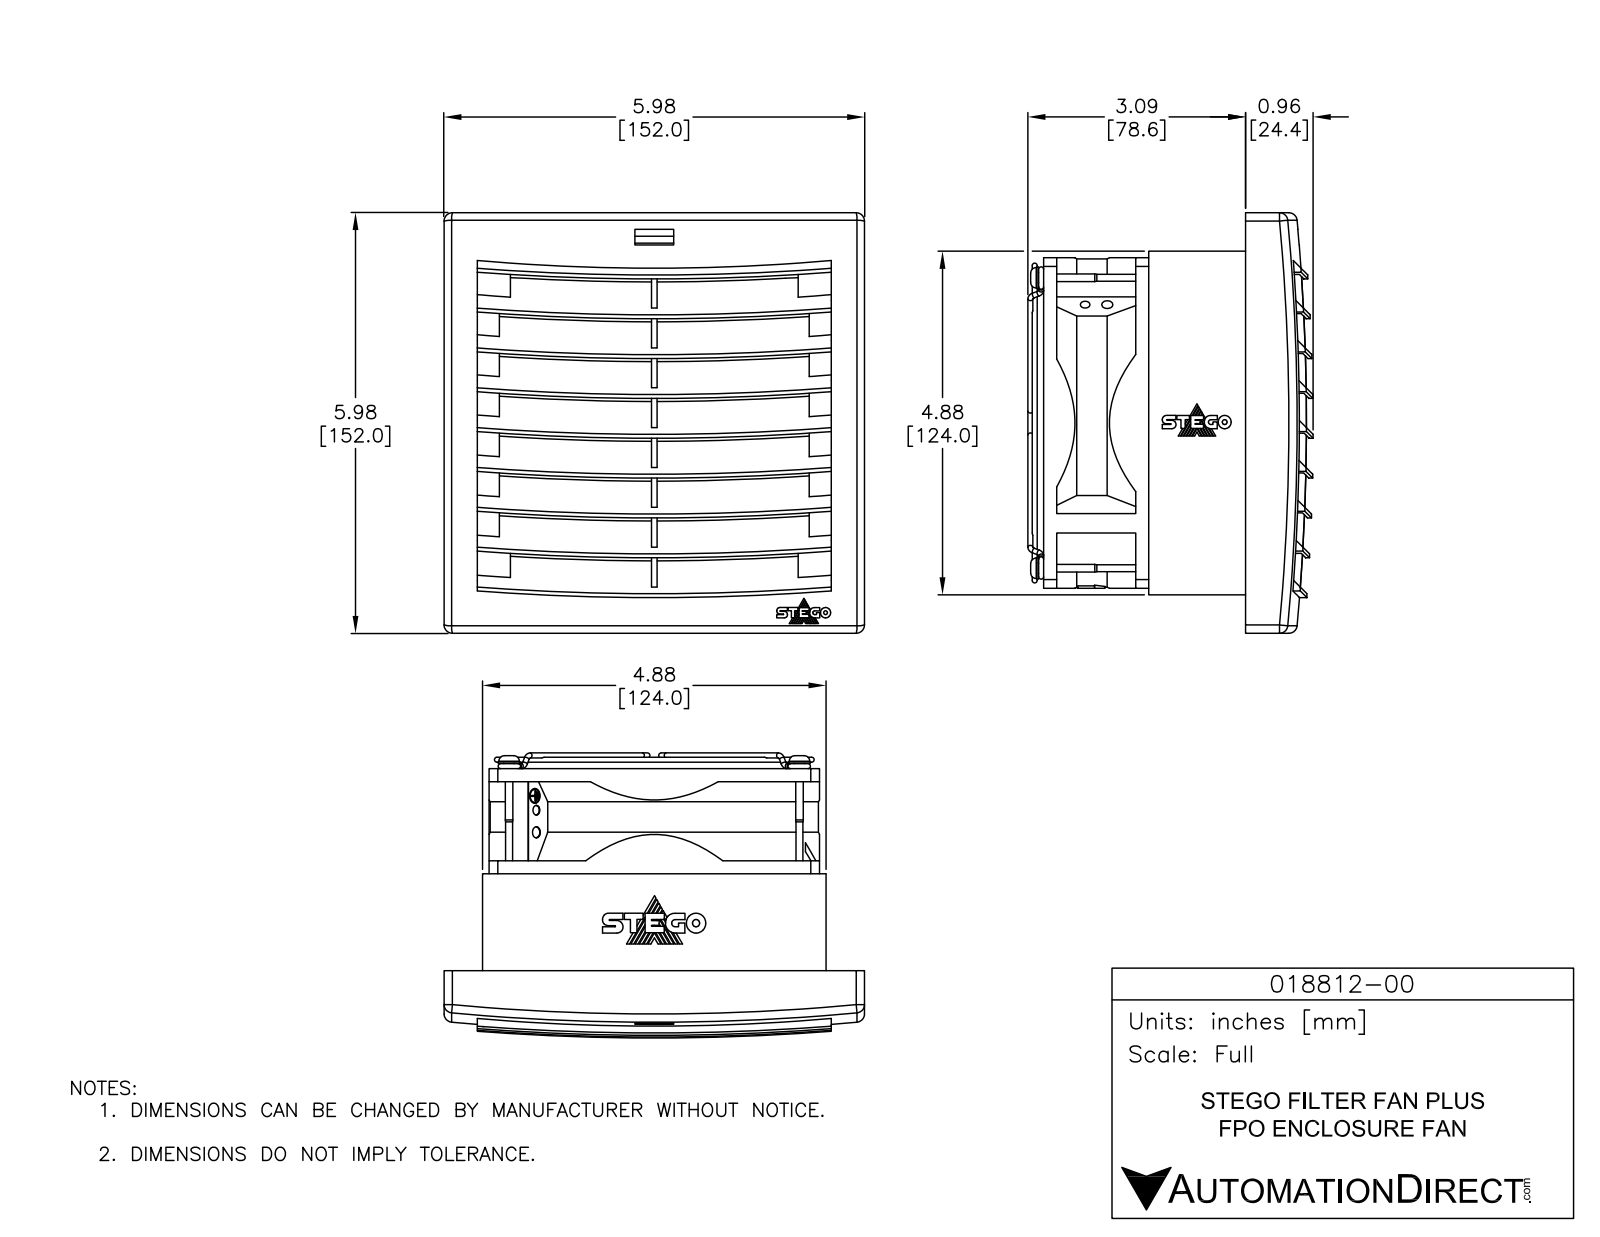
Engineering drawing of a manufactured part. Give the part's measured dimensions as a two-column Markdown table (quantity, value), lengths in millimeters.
| quantity | value |
| --- | --- |
| part name | 018812-00 |
| STEP written by | SolidWorks 2018 (AUTOMOTIVE_DESIGN) |
| units | millimeters |
| bodies | 1 solid, 544 faces (329 planar, 207 cylindrical, 8 other) |
| overall size | 152 × 152 × 104 |
| volume | 537 000 mm³ |
| surface area | 231 900 mm² |
| round holes (diameter × count) | 6.5 × 4, 24.9 × 1, 42.2 × 1, 59.4 × 1, 76.7 × 1, 82.6 × 1, 96 × 1, 105.4 × 1 |
| round bosses / shafts (diameter × count) | 110.4 × 1, 88.6 × 1, 80.7 × 1, 68.9 × 1, 63.4 × 1, 46.2 × 1, 33.6 × 1, 28.9 × 1 |
| partial cylindrical surfaces (radius × count) | 349.4 × 16, 47 × 5, 3 × 4, 3.6 × 4, 13.2 × 1, 21.6 × 1, 24.6 × 1, 31.4 × 1 |
| main face-to-face distances | 1.5, 10.8, 3.1, 120.9, 21.6, 2, 3.4, 6.8, 12.3, 9.3 |
| hole center spacings | 76.4, 108, 152.7 |
